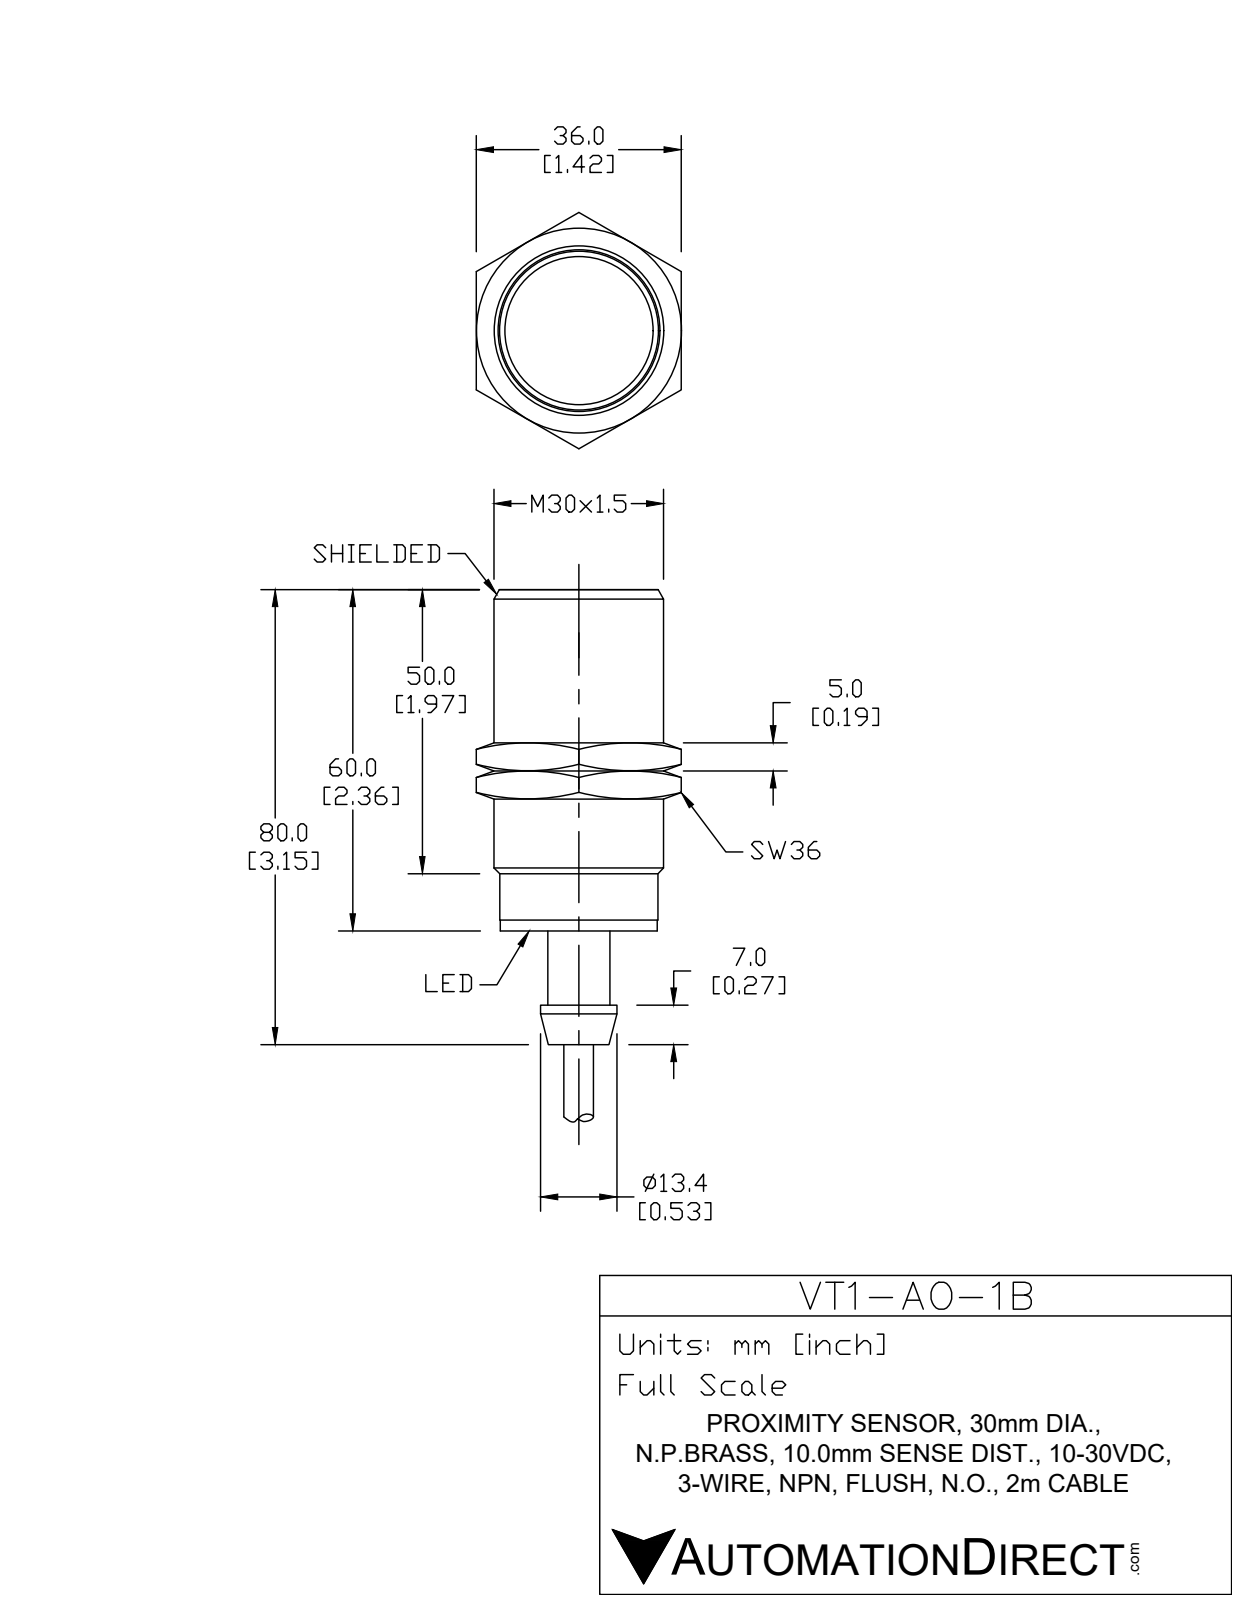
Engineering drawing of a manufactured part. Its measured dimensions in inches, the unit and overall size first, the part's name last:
Units: inches
Overall size (bounding box): 3.858 × 1.181 × 1.181
Round holes (diameter × count): ⌀0.224 ×1, ⌀0.917 ×1, ⌀1.016 ×1
Round bosses / shafts (diameter × count): ⌀1.181 ×1, ⌀1.094 ×1, ⌀1.018 ×1, ⌀1.014 ×1, ⌀0.99 ×1, ⌀0.531 ×1, ⌀0.433 ×1, ⌀0.217 ×1
Main face-to-face distances: 2.283, 0.118, 2.165, 0.079, 2.362, 2.244, 0.045, 0.073, 2.238, 2.317
Volume: 2.716 in³ · Surface area: 22.99 in²
Bodies: 4 solids, 48 faces (14 planar, 24 cylindrical, 10 other)
Part name (STEP PRODUCT): VT1-A0-1B
STEP written by: SolidWorks 2017 (AUTOMOTIVE_DESIGN)
